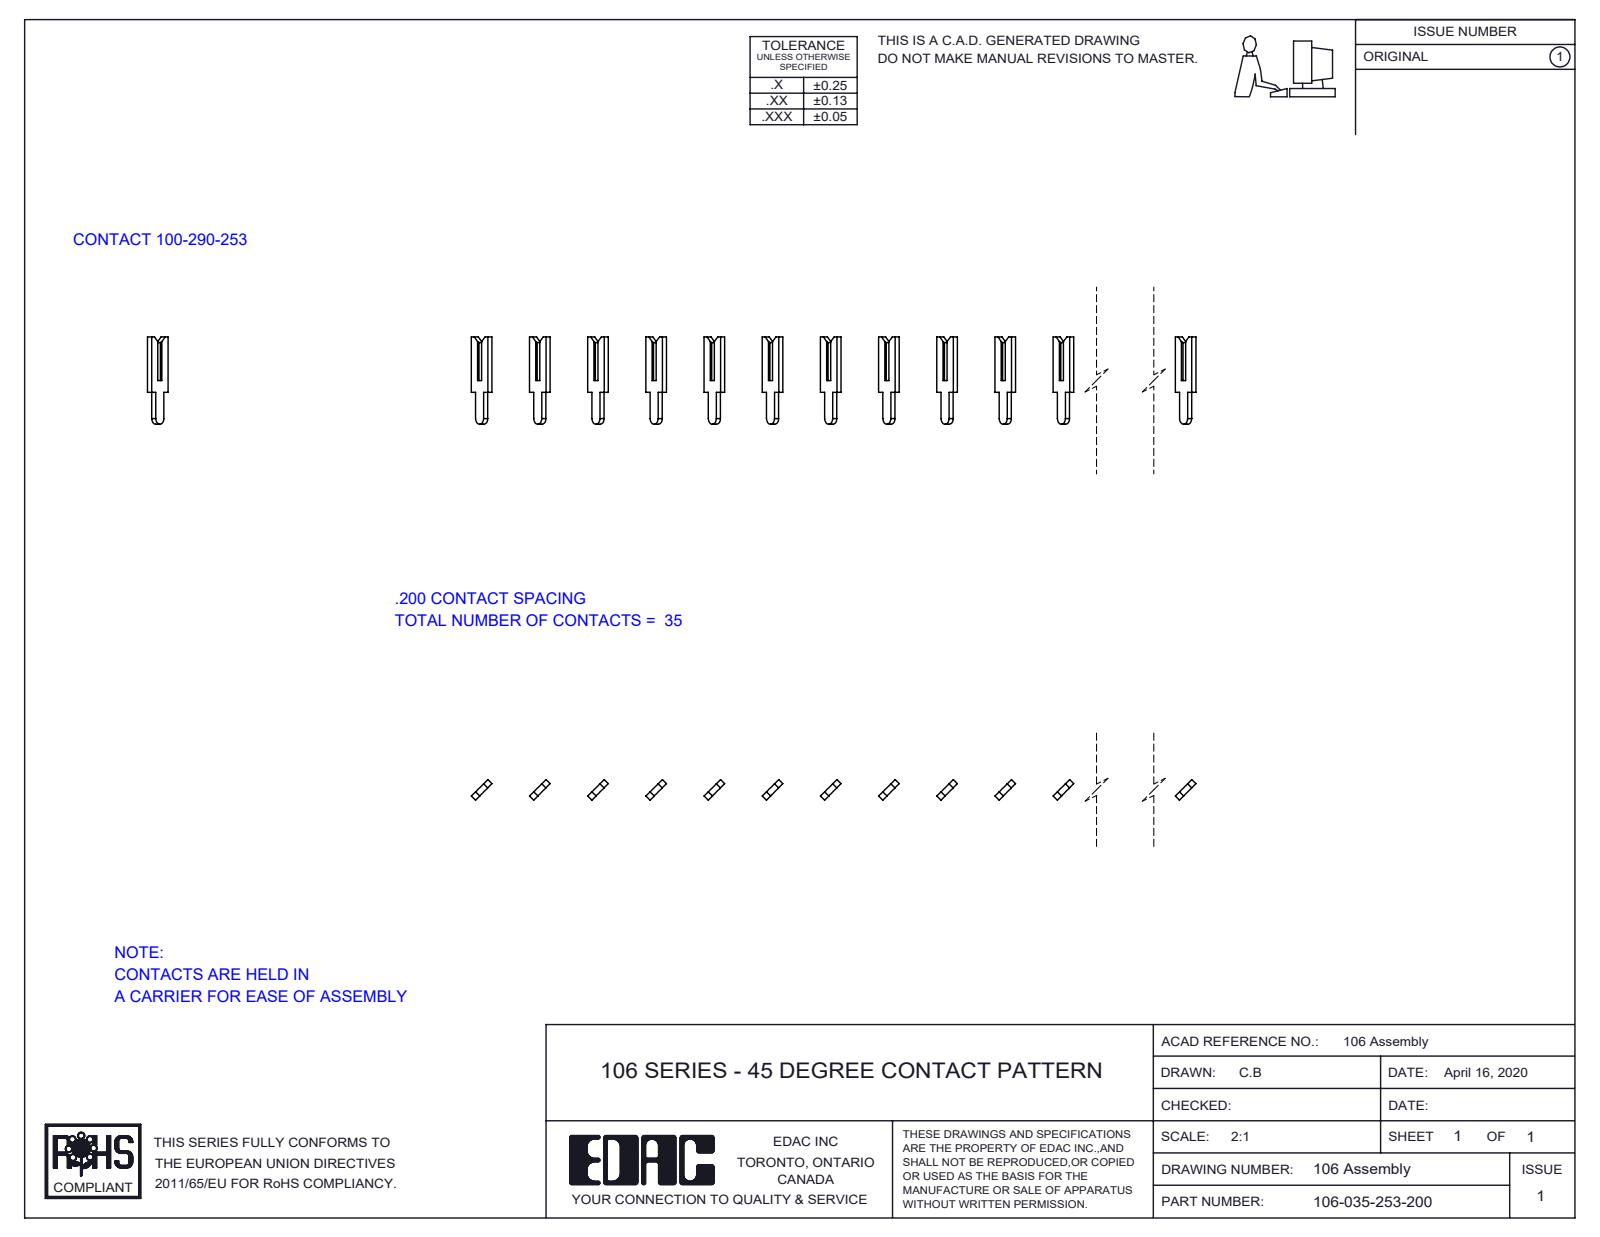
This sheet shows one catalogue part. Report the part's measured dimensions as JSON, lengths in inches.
{"part_name": "100-290-001_100-290-253; 106-035-253-200", "step_written_by": "SolidWorks 2016 (CONFIG_CONTROL_DESIGN)", "units": "inches", "bodies": {"solids": 35, "faces": 700, "planar": 665, "cylindrical": 35, "other": 0}, "overall_size": [6.871, 0.3, 0.071], "volume_in3": 0.012, "surface_area_in2": 1.867, "partial_cylinders_radius": [[0.019, 35]], "face_to_face_distances": [0.141, 0.848, 0.283, 0.99, 0.707, 0.566, 0.424, 1.131, 0.424, 1.838]}
